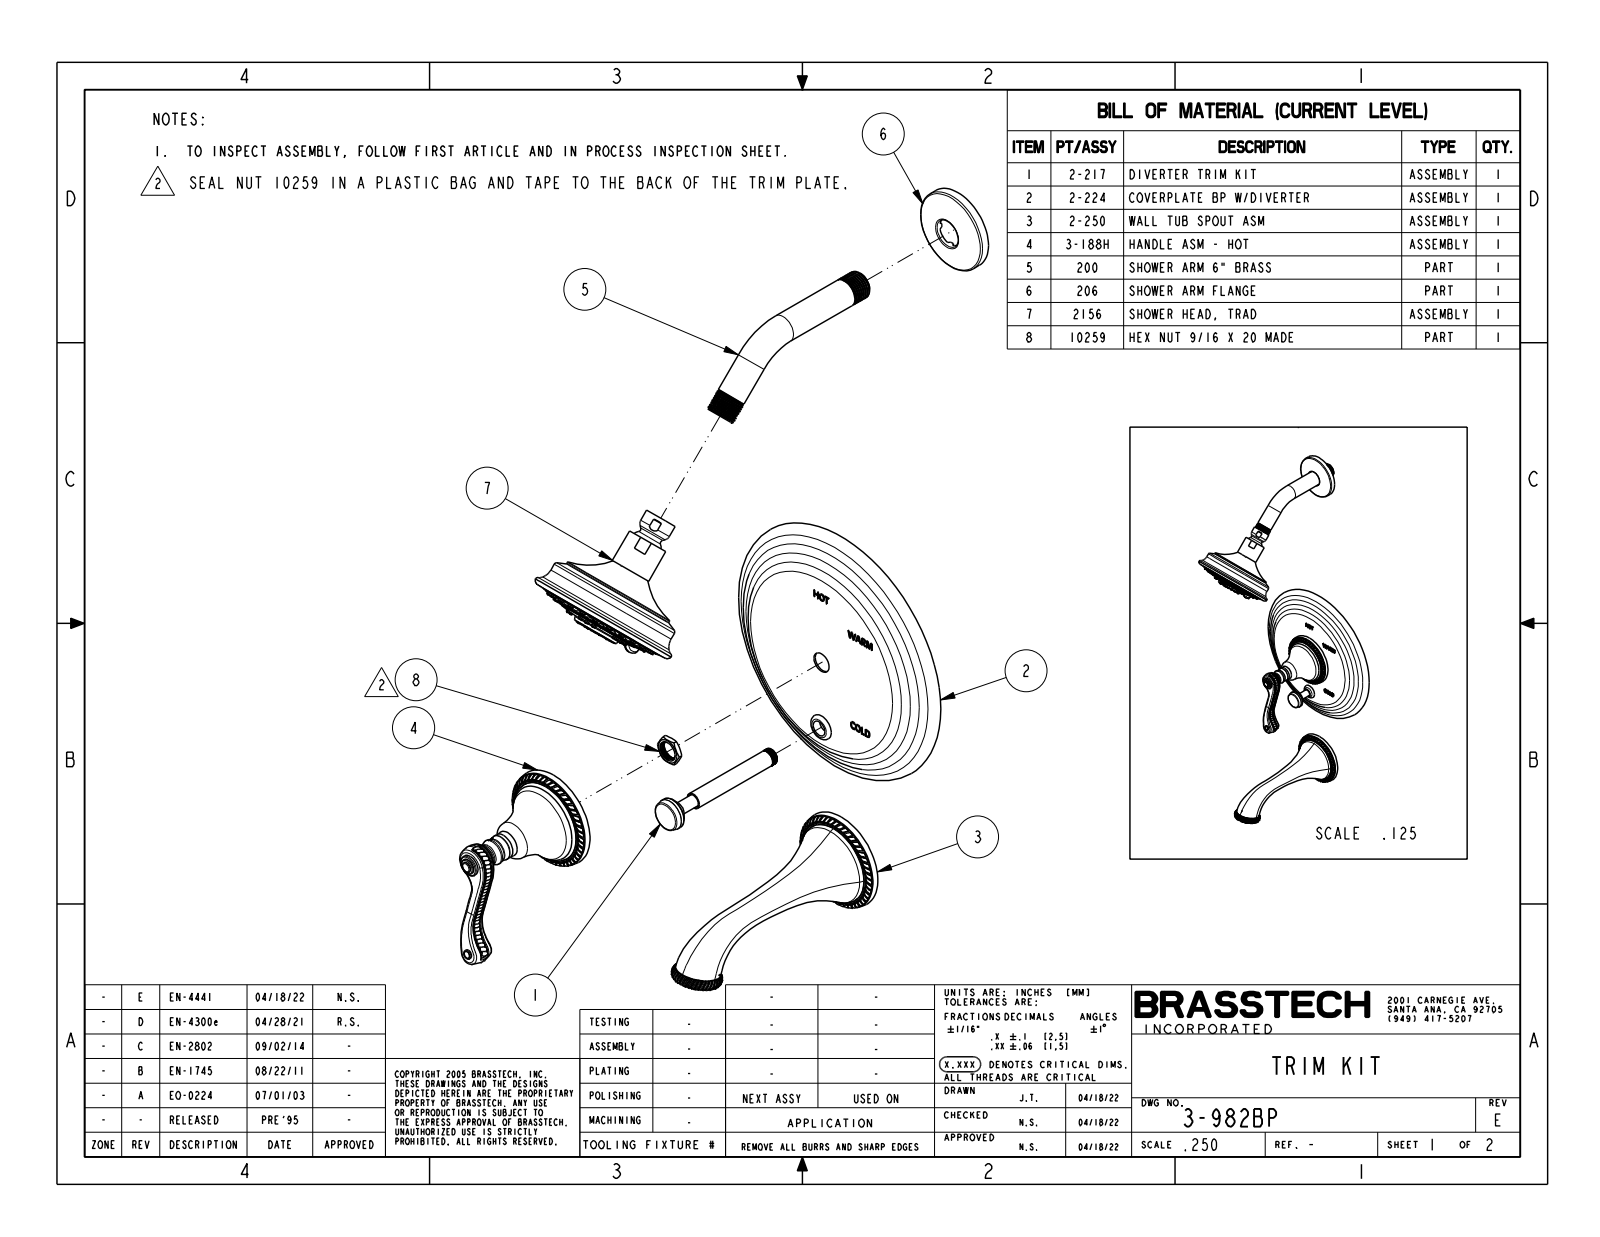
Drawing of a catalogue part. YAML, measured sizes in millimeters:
part_name: "3-982BP"
step_written_by: "CREO PARAMETRIC BY PTC INC, 2018400 (CONFIG_CONTROL_DESIGN)"
units: millimeters
bodies: {solids: 3, faces: 2622, planar: 494, cylindrical: 500, other: 1628}
overall_size: [548.9, 209.6, 196.9]
volume: 1020000
surface_area: 149600
round_holes:
  - {diameter: 1.5, count: 8}
  - {diameter: 23.5, count: 1}
round_bosses_or_shafts:
  - {diameter: 3.6, count: 39}
  - {diameter: 4.2, count: 23}
  - {diameter: 20.7, count: 2}
  - {diameter: 6.6, count: 2}
  - {diameter: 96.8, count: 1}
  - {diameter: 94.6, count: 1}
  - {diameter: 82.3, count: 1}
  - {diameter: 60.5, count: 1}
partial_cylinders:
  - {radius: 3.8, count: 98}
  - {radius: 2.3, count: 50}
  - {radius: 3, count: 48}
  - {radius: 5.7, count: 40}
  - {radius: 2, count: 8}
  - {radius: 0.5, count: 2}
  - {radius: 3.1, count: 2}
  - {radius: 3.5, count: 2}
face_to_face_distances: [19.2, 1.6, 3, 4.6, 101.2, 82, 64.8, 45.7, 36.4, 61.3]
hole_center_spacings: [11.3, 14.7, 20.8, 20.8, 27.2, 11.3, 14.7, 27.2]
